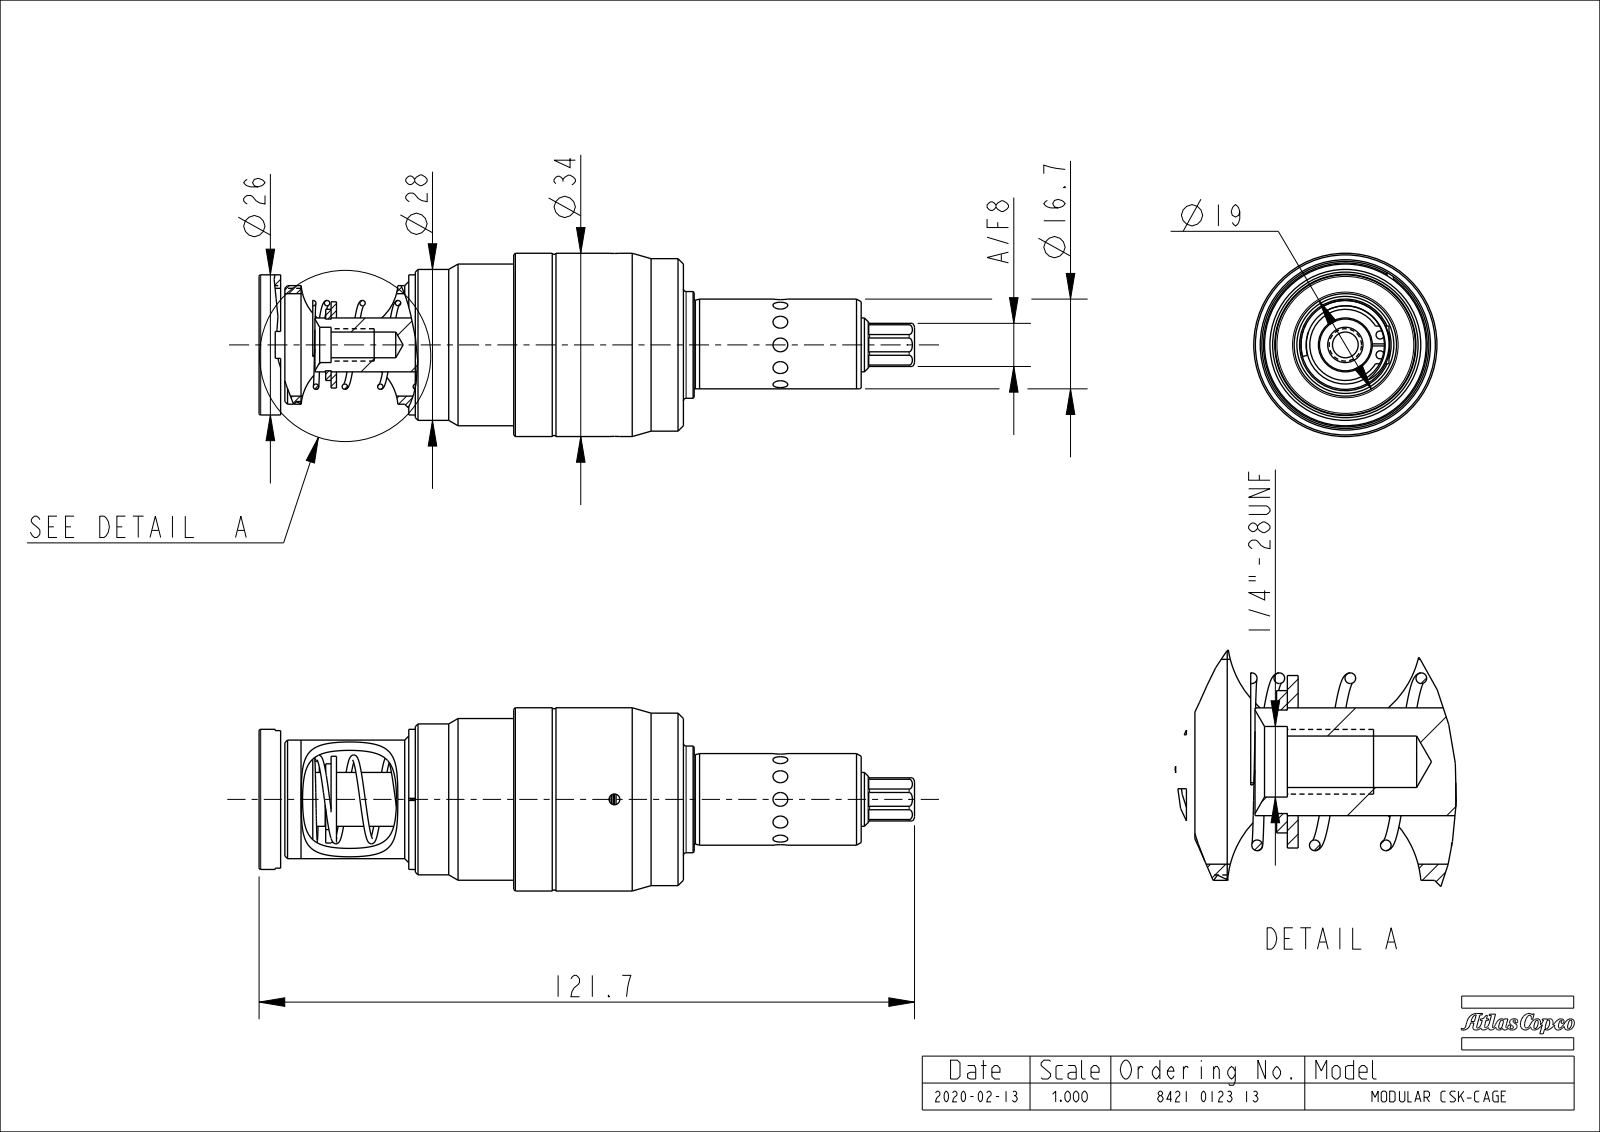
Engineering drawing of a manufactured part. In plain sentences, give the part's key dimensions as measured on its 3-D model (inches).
The part is named "EXT_COMP_SW0045". Its 3-D file was written by "CREO PARAMETRIC BY PTC INC, 2018100 (AP242_MANAGED_MODEL_BASED_3D_ENGINEERING_MIM_LF)". It is 4 solids with 355 faces: 93 planar, 114 cylindrical and 148 other. Overall it measures 6.483 by 1.339 by 1.339 inches. Its volume is 3.207 cubic inches and its surface area 27.56 square inches. Round holes: 2 of diameter 0.059, 1 of diameter 0.039, 1 of diameter 0.079, 1 of diameter 0.188, 1 of diameter 0.258, 1 of diameter 0.748, 1 of diameter 0.827, 1 of diameter 0.866, 1 of diameter 1.031. Round bosses or shafts: 1 of diameter 1.339, 1 of diameter 1.26, 1 of diameter 1.181, 1 of diameter 1.102, 1 of diameter 1.024, 1 of diameter 0.925, 1 of diameter 0.906, 1 of diameter 0.78. Partial cylindrical surfaces (rounded edges, fillets, slot ends): 18 of radius 0.039, 6 of radius 0.118, 2 of radius 0.354, 1 of radius 0.165, 1 of radius 0.189, 1 of radius 0.61. The main face-to-face distances are 0.787, 0.157, 0.039, 1.575, 0.63, 0.118, 0.945, 3.101, 3.889, 2.076. The hole center spacings are 0.264, 0.145.
